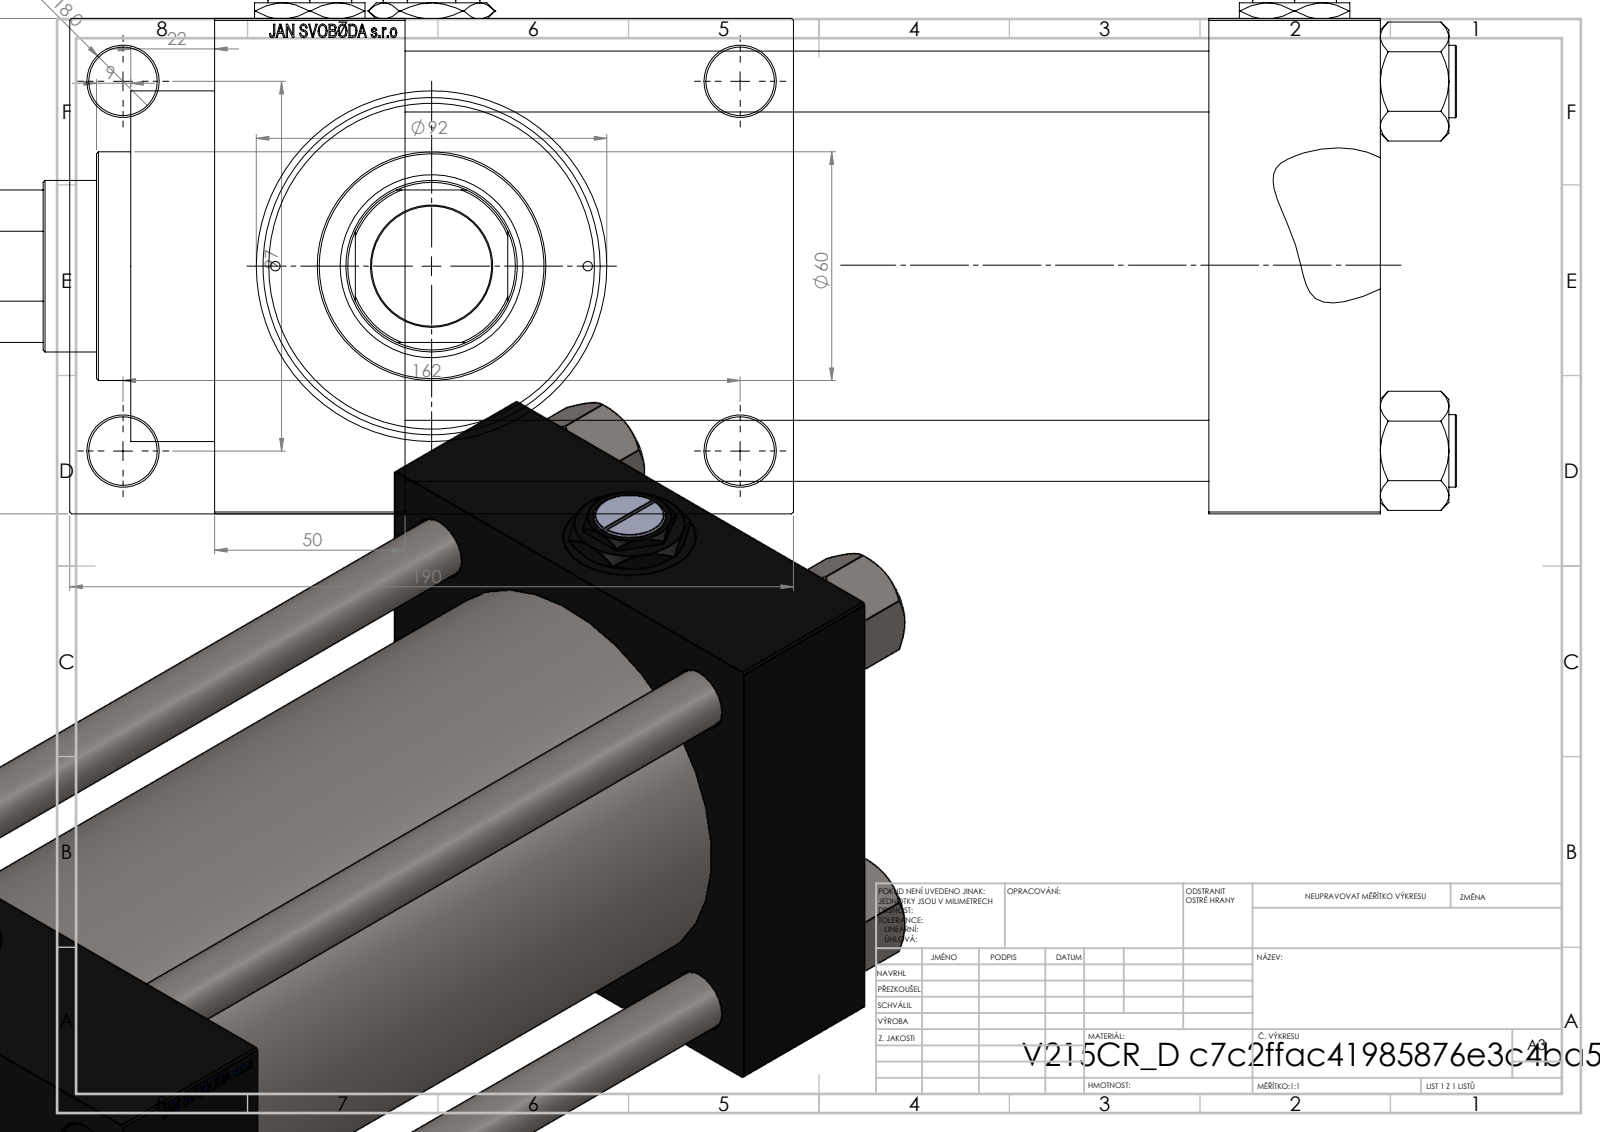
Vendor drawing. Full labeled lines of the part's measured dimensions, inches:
Part name (STEP PRODUCT): NUT_M5_D; V215_VC_A; V215CR_D_TYCINKA; V215CR_D_Body (+2 more)
STEP written by: SolidWorks 2019 (CONFIG_CONTROL_DESIGN)
Units: inches
Bodies: 13 solids, 1260 faces (595 planar, 103 cylindrical, 562 other)
Overall size (bounding box): 15.079 × 7.48 × 5.394
Volume: 185.9 in³ · Surface area: 775.3 in²
Round holes (diameter × count): ⌀0.63 ×4, ⌀0.709 ×4, ⌀1.041 ×4, ⌀1.378 ×4, ⌀0.276 ×3, ⌀0.098 ×2, ⌀1.24 ×1, ⌀1.772 ×1, ⌀1.89 ×1, ⌀2.992 ×1, ⌀3.366 ×1, ⌀3.937 ×1
Round bosses / shafts (diameter × count): ⌀0.748 ×4, ⌀4.173 ×1, ⌀3.622 ×1, ⌀2.362 ×1
Partial cylindrical surfaces — rounded edges, fillets, slot ends (radius × count): R0.866 ×1
Main face-to-face distances: 1.772, 5.118, 10.079, 8.307, 12.047, 10.276, 1.969, 6.299, 1.181, 3.78
Hole centre spacings: 1.281, 1.93, 2.475, 2.698, 3.717, 3.815, 4.005, 4.026
